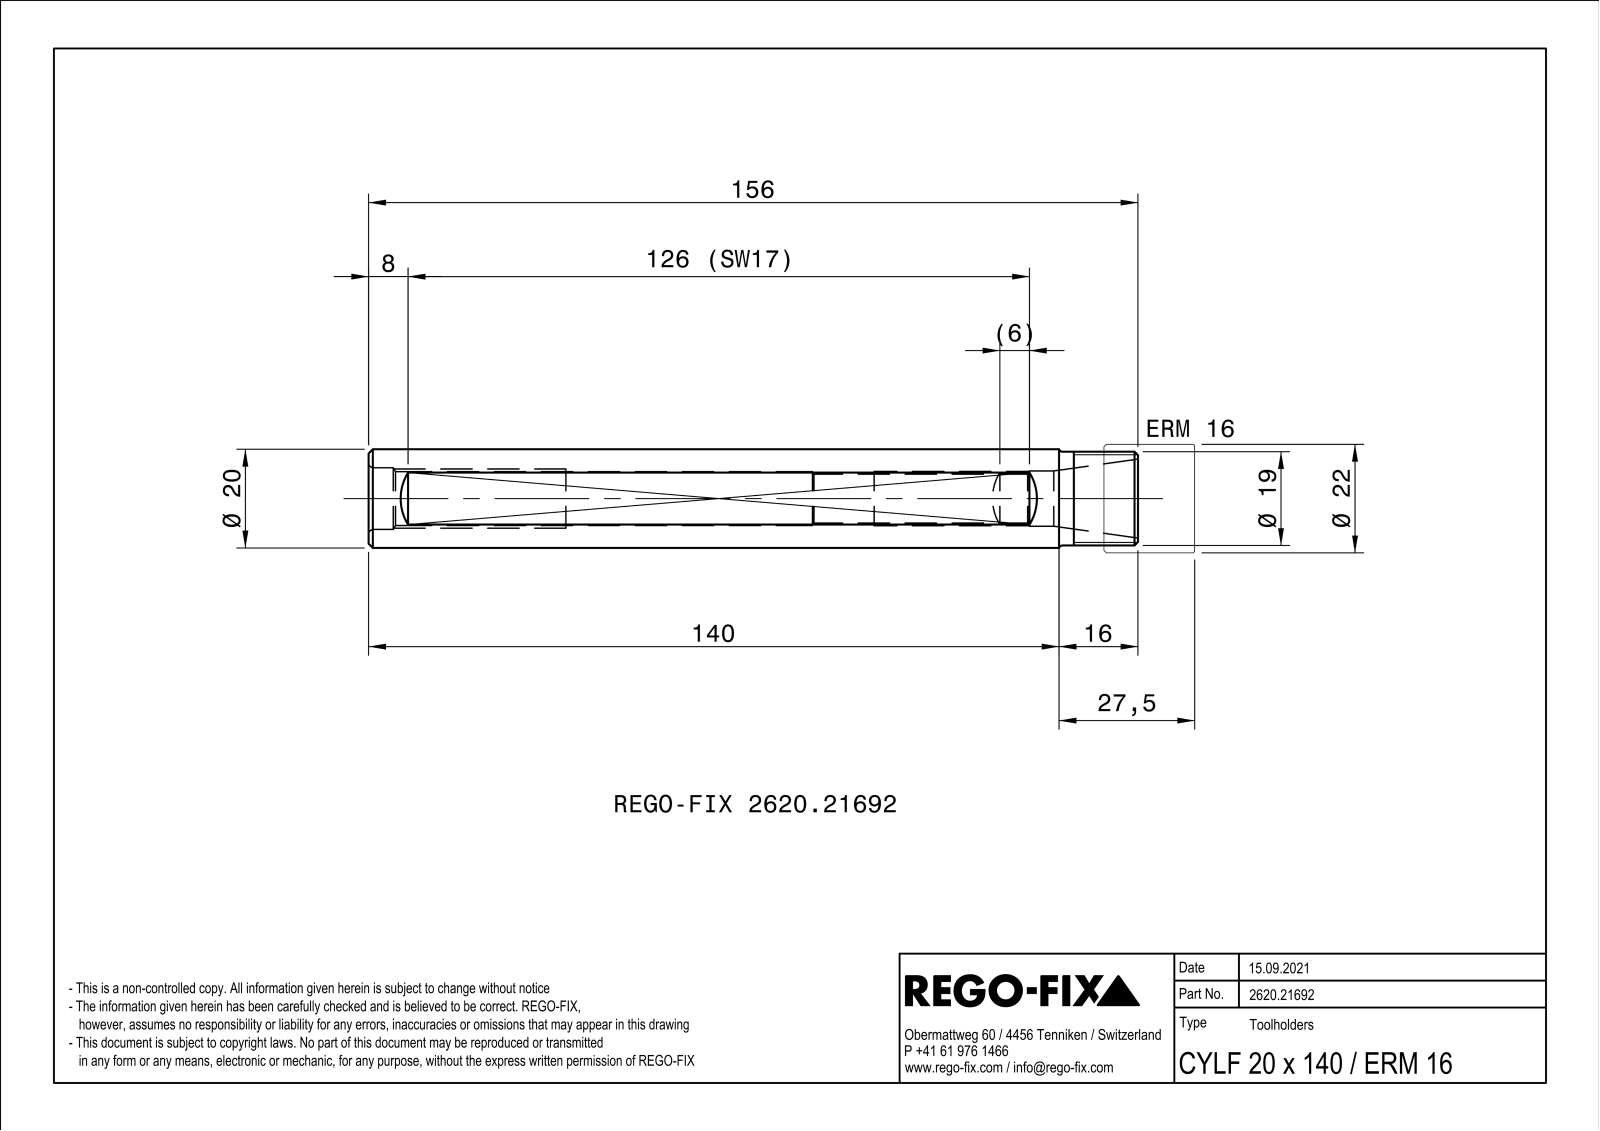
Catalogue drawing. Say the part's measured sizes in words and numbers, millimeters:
The part is named "NOCUT". Its 3-D file was written by "SIEMENS PLM Software Solid Edge ST10 (AUTOMOTIVE_DESIGN)". It is 1 solid with 26 faces: 8 planar, 9 cylindrical and 9 other. Overall it measures 156 by 20 by 20 millimeters. Its volume is 32 065 cubic millimeters and its surface area 15 332 square millimeters. Round holes: 1 of diameter 9.92, 1 of diameter 10.92, 1 of diameter 11.2, 1 of diameter 12.5. Round bosses or shafts: 1 of diameter 20, 1 of diameter 19. The main face-to-face distances are 17, 156, 77.07, 7.77.
